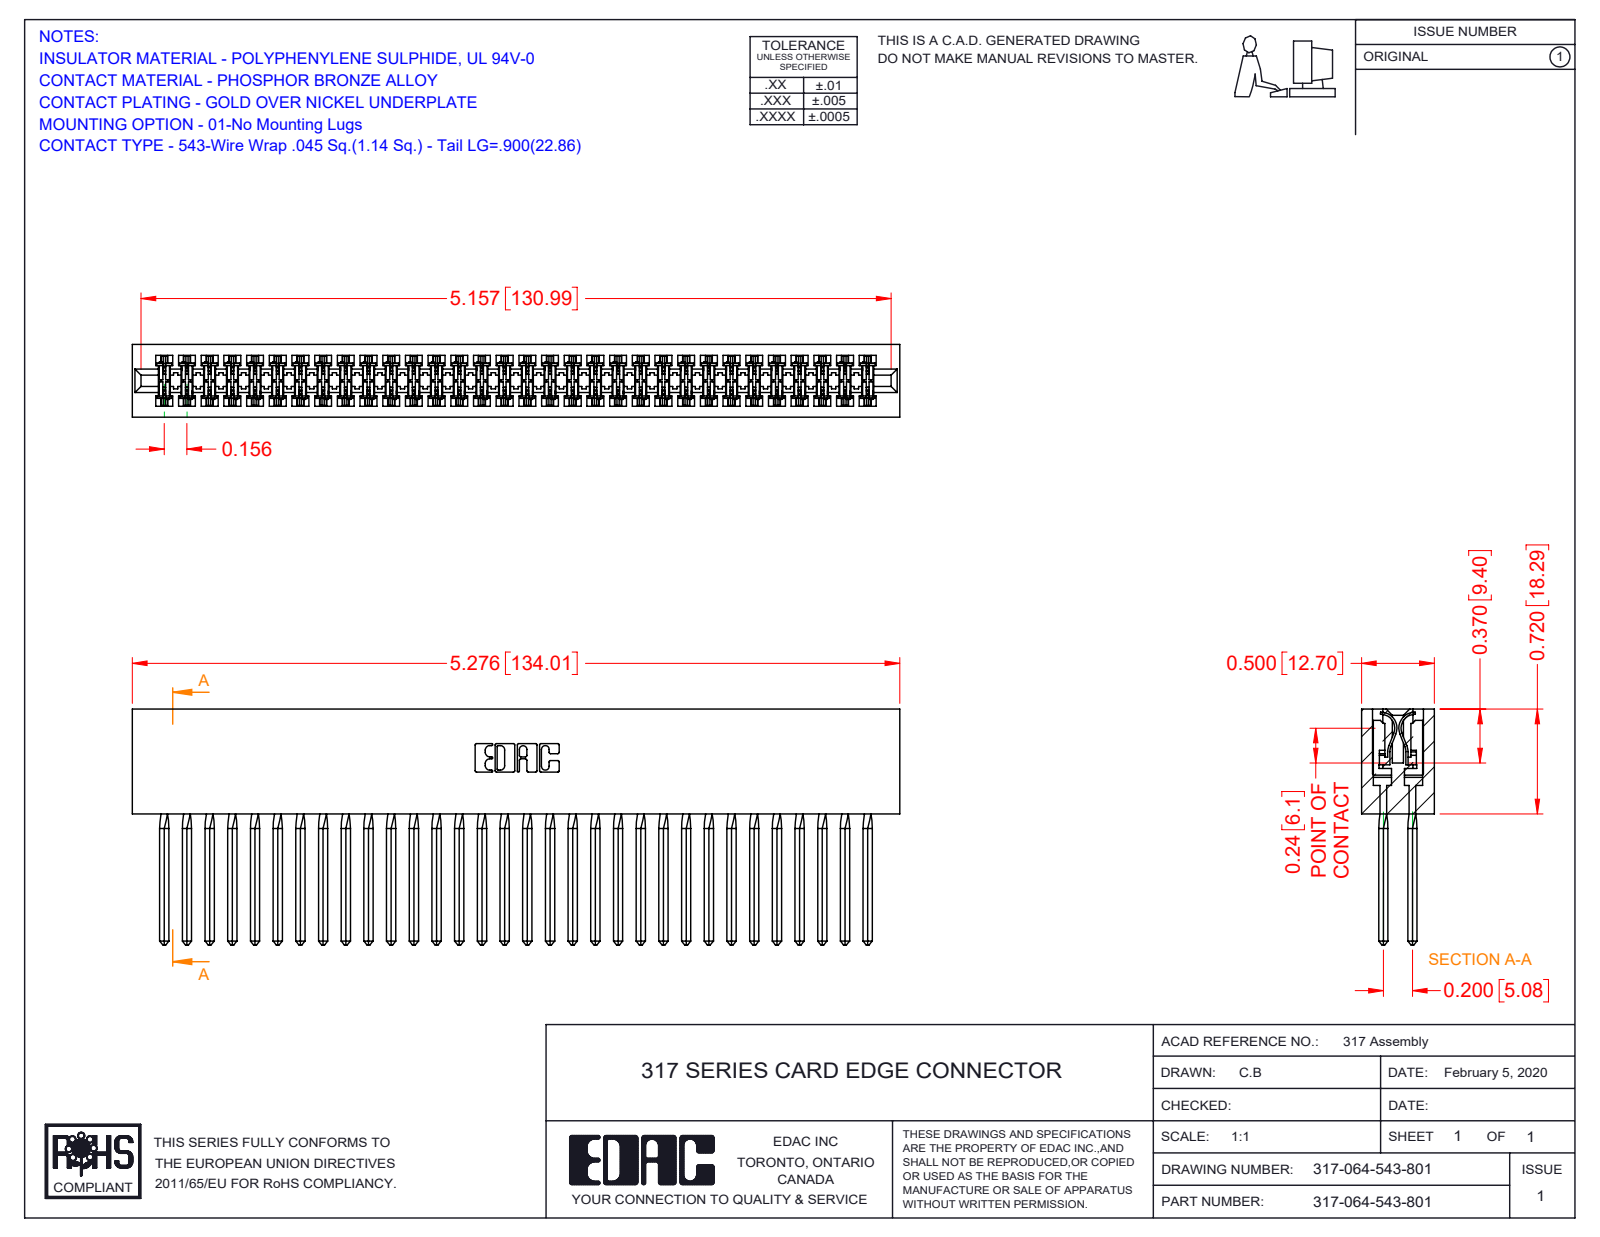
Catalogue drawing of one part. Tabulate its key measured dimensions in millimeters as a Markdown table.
| quantity | value |
| --- | --- |
| part name | 317 Part_Lugless; 317-064-543-801; 317-290-001_543 |
| STEP written by | SolidWorks 2016 (CONFIG_CONTROL_DESIGN) |
| units | millimeters |
| bodies | 65 solids, 5786 faces (4722 planar, 808 cylindrical, 256 other) |
| overall size | 134 × 41.1 × 12.7 |
| volume | 24 270 mm³ |
| surface area | 36 700 mm² |
| partial cylindrical surfaces (radius × count) | 0.4 × 128, 0.3 × 22, 0.2 × 6, 0.8 × 6, 0.7 × 3, 2.4 × 2, 2.5 × 2, 2.8 × 2 |
| main face-to-face distances | 1.9, 12.7, 10.8, 8.9, 2.8, 5, 2.4, 5.1, 2.9, 3.3 |
